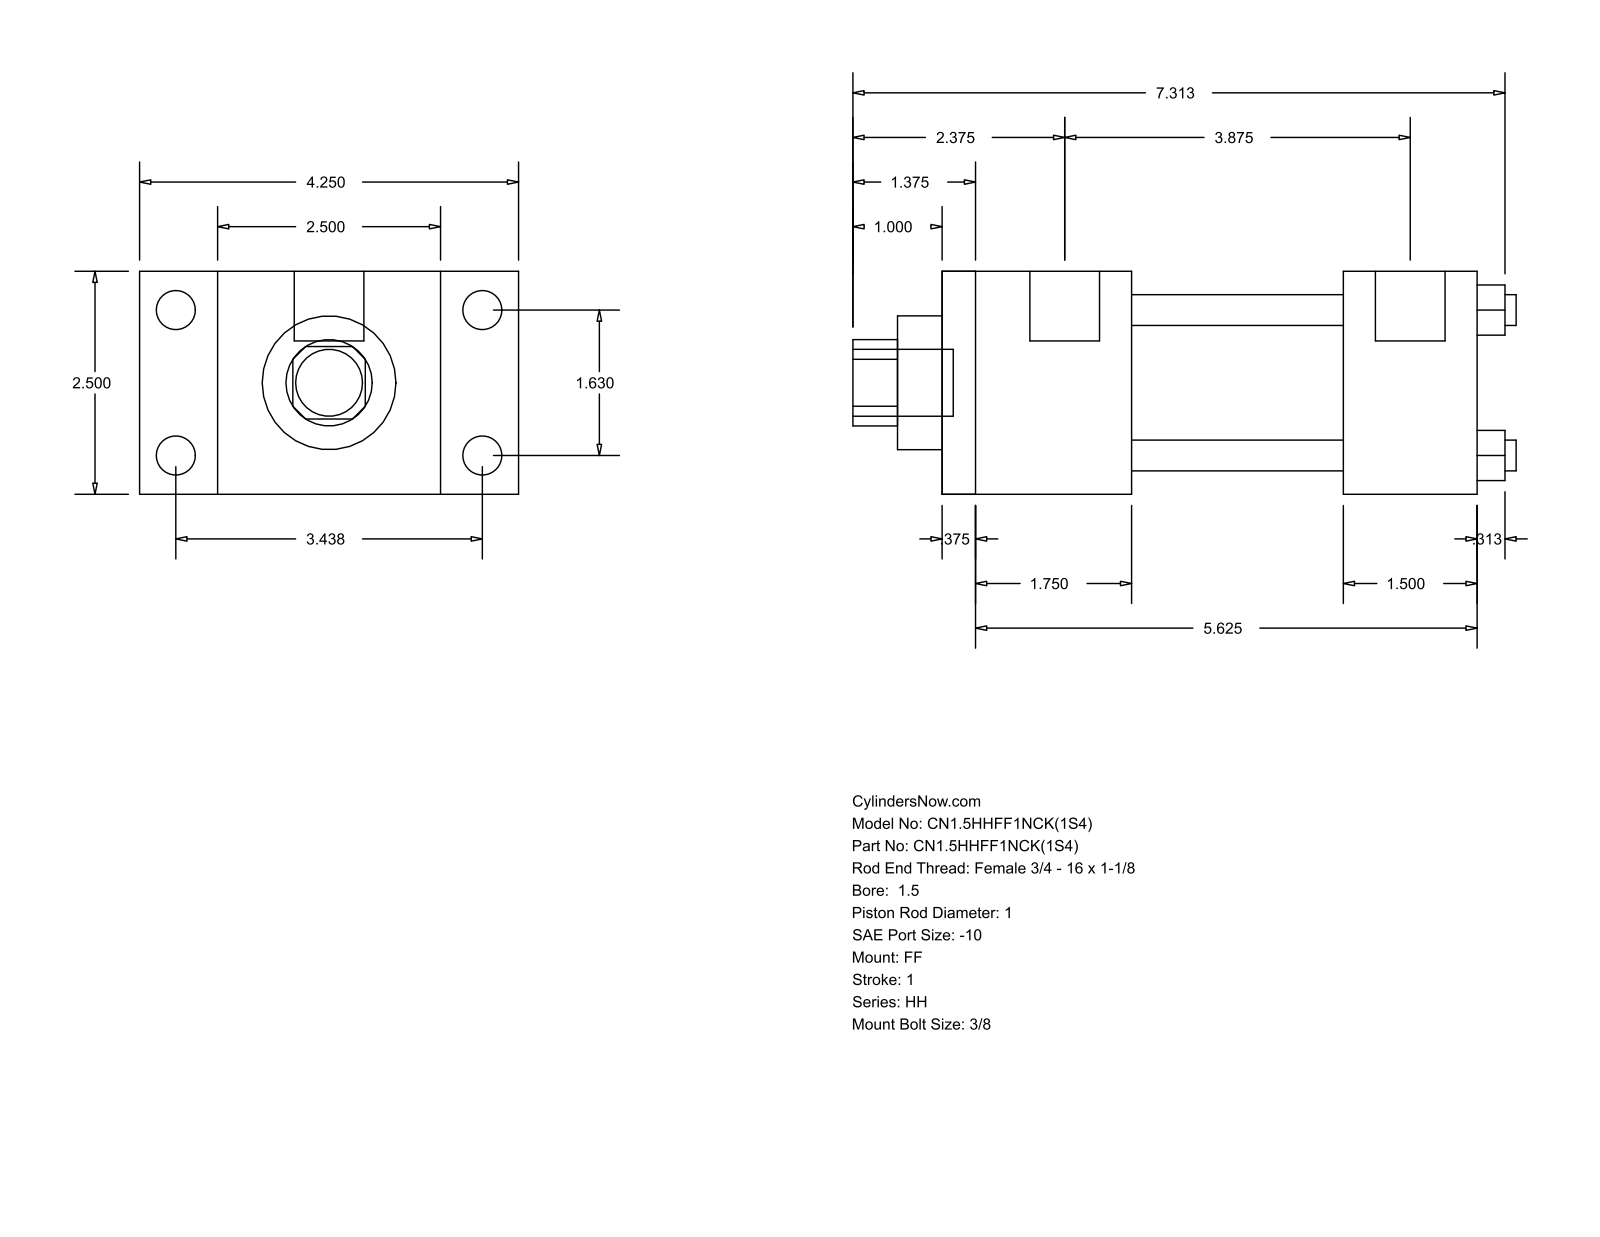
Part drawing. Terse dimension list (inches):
name: HH_FF__0150_1
written by: GSSL Pune (CONFIG_CONTROL_DESIGN)
unit: in
bodies: 0 solids, 92 faces (64 planar, 28 cylindrical, 0 other)
size: 7.437 × 4.25 × 2.5
holes: 4× ⌀0.345, 1× ⌀1, 1× ⌀1.5, 1× ⌀1.75
bosses: 4× ⌀0.438, 4× ⌀0.219, 2× ⌀0.781, 1× ⌀0.75
rounds: 1× R0.484
face distances: 2.5, 6, 0.375, 5.625, 2.125, 1.75, 3.875, 4.5, 4.125, 2.375
hole spacings: 1.152, 1.63, 2.305
